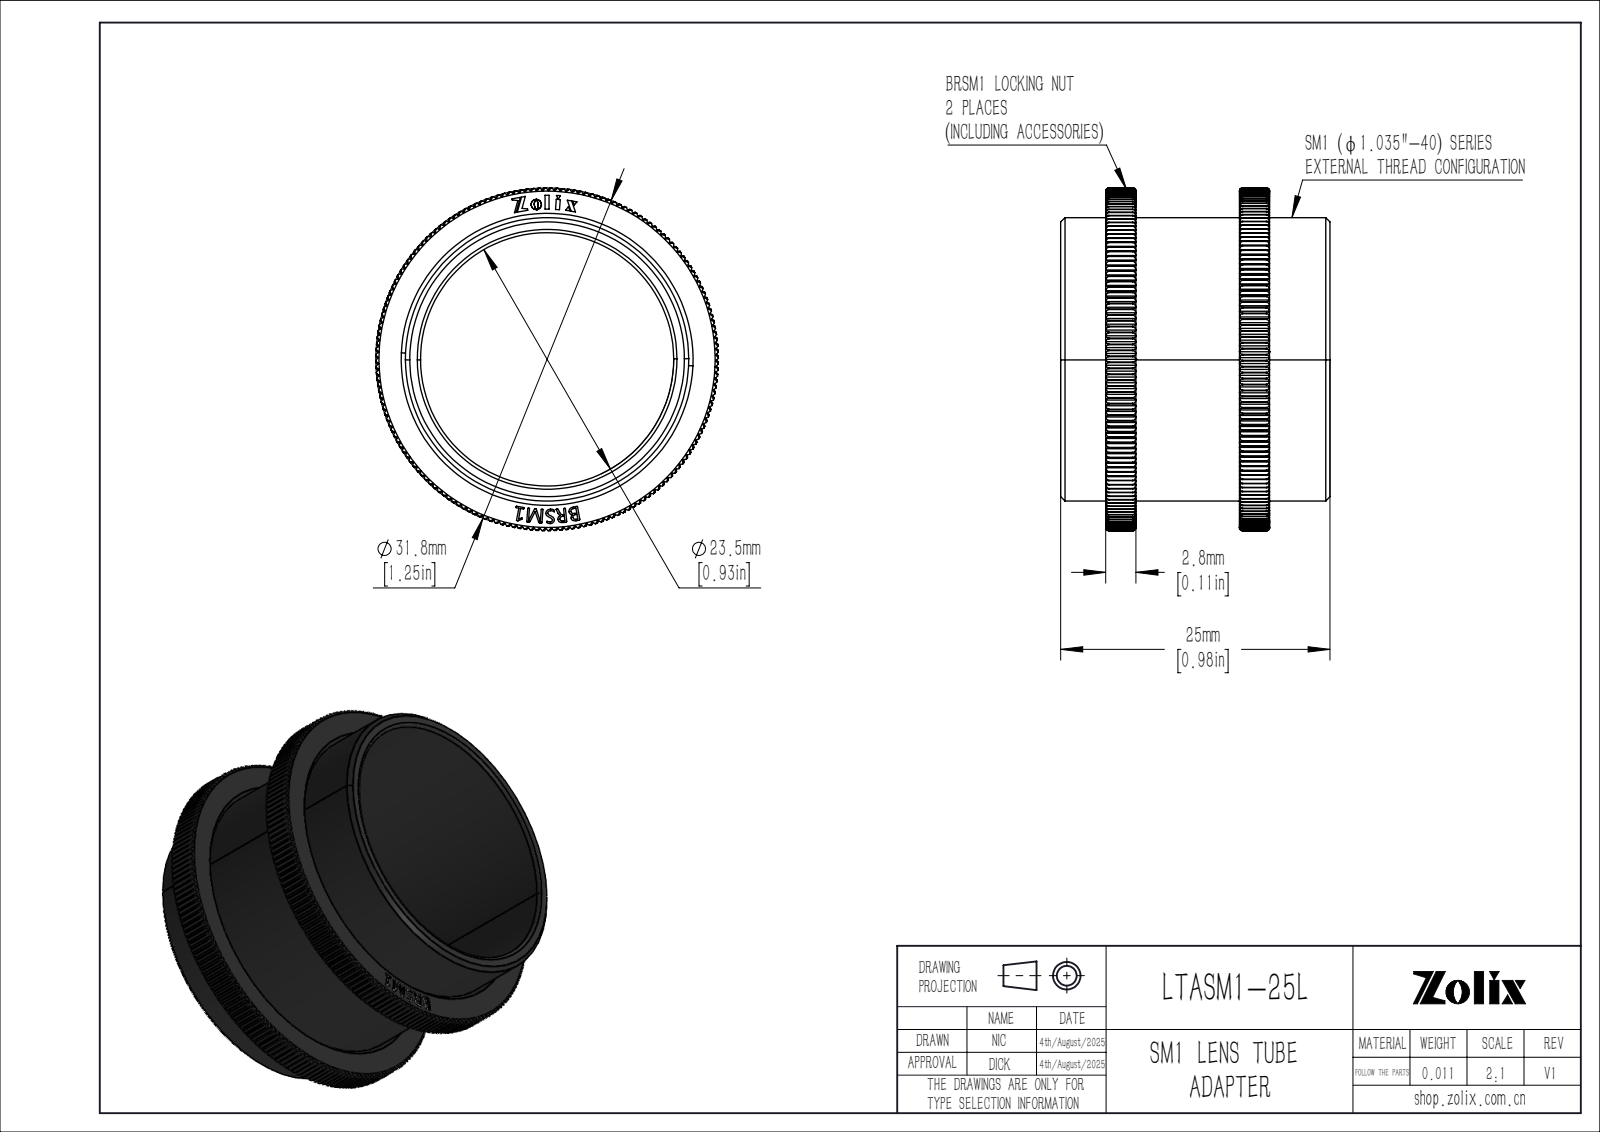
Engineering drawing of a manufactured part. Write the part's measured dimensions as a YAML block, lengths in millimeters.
part_name: "LTASM1-25L"
step_written_by: "SolidWorks 2020 (CONFIG_CONTROL_DESIGN)"
units: millimeters
bodies: {solids: 3, faces: 1664, planar: 1164, cylindrical: 368, other: 132}
overall_size: [31.8, 31.8, 25]
volume: 4027
surface_area: 6151
round_holes:
  - {diameter: 23.5, count: 1}
  - {diameter: 26.29, count: 1}
partial_cylinders:
  - {radius: 15.9, count: 1}
face_to_face_distances: [2.8, 12.4, 9.6, 15.2, 22.13, 22.14, 22.12, 4.19, 6.99, 16.59]
